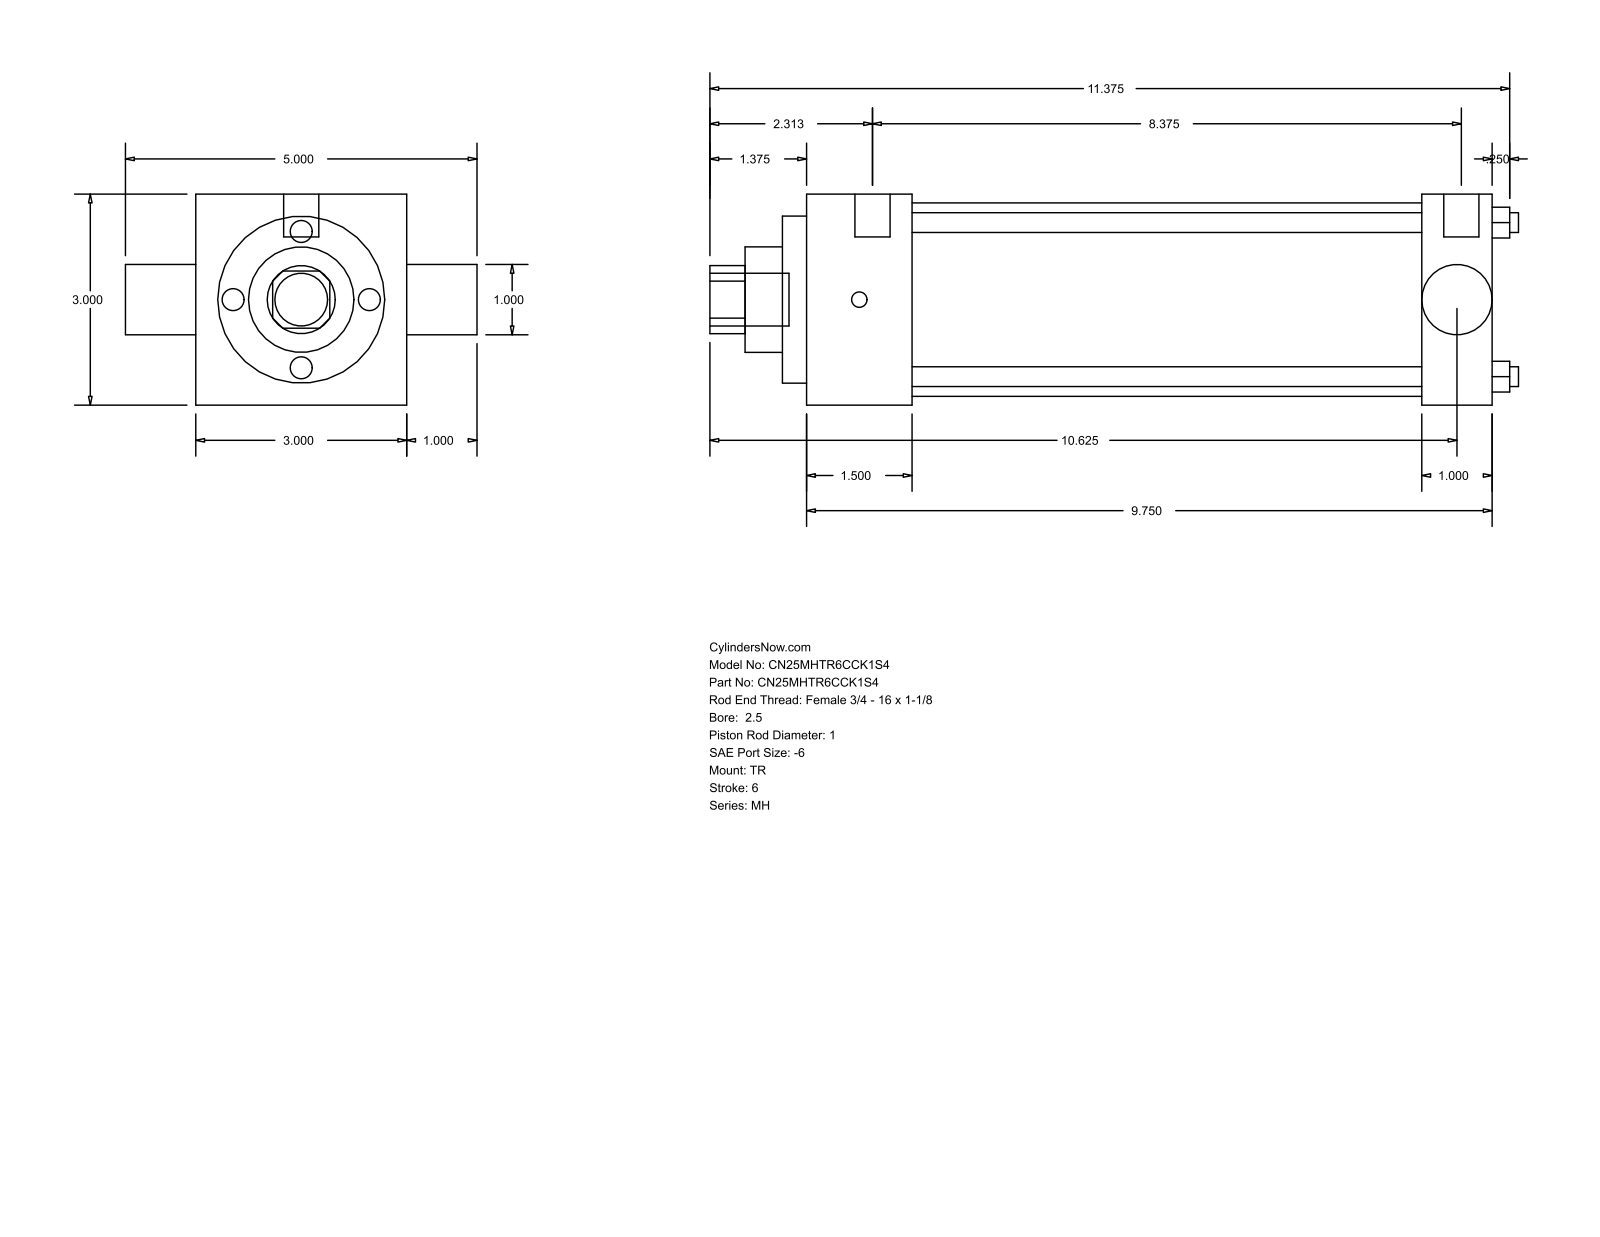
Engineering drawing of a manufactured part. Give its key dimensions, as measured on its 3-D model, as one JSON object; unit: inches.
{"part_name": "MH_TR__0250_1", "step_written_by": "GSSL Pune (CONFIG_CONTROL_DESIGN)", "units": "inches", "bodies": {"solids": 0, "faces": 86, "planar": 61, "cylindrical": 25, "other": 0}, "overall_size": [11.5, 5, 3], "round_holes": [[0.281, 4], [0.998, 1], [1, 1], [1.5, 1], [2.375, 1], [2.75, 1]], "round_bosses_or_shafts": [[0.219, 3], [0.5, 2], [0.75, 1]], "partial_cylinders_radius": [[0.484, 1]], "face_to_face_distances": [3, 9.75, 1, 1.5, 8.25, 8.75, 7.25, 0.344, 1.844, 9.094], "hole_center_spacings": [1.548, 2.19, 3.097]}
